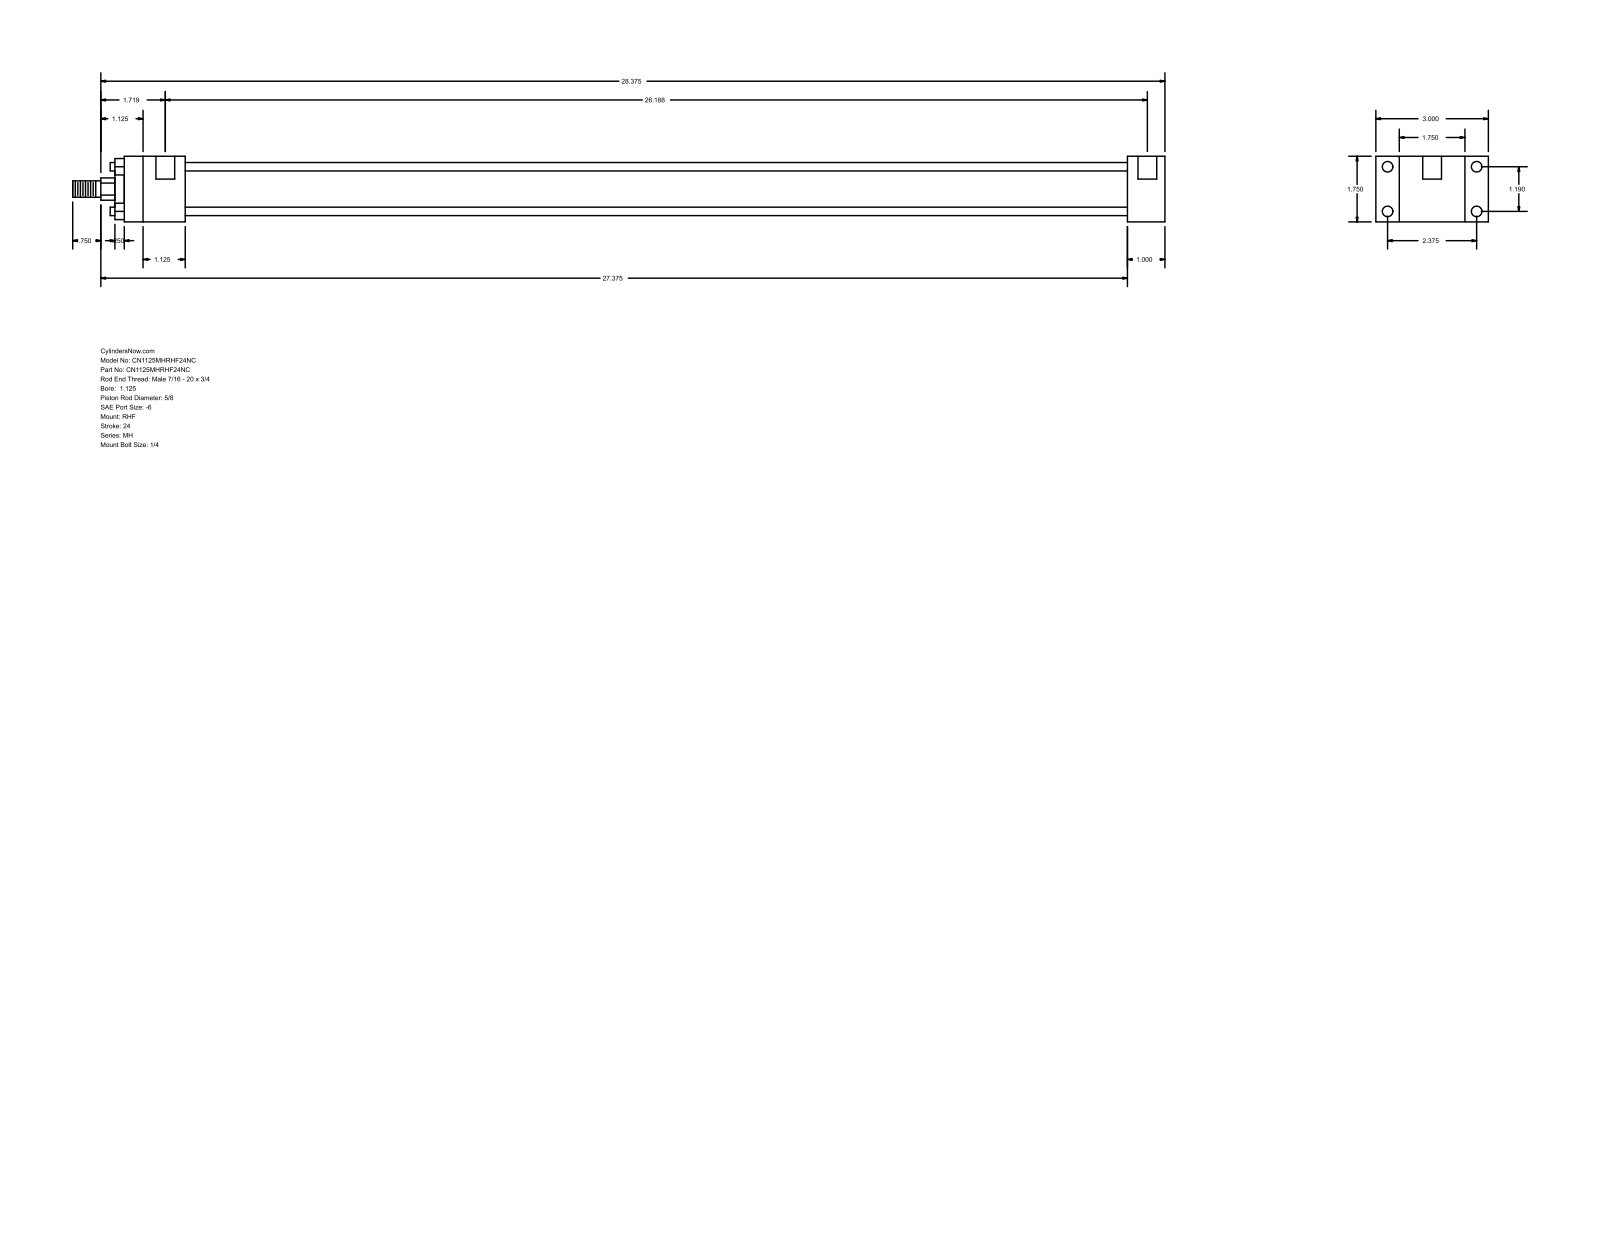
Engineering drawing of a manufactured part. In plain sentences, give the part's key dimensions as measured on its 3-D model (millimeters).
The part is named "MH_RHF__0112_0.625". Its 3-D file was written by "GSSL Pune (CONFIG_CONTROL_DESIGN)". It is 0 solids with 88 faces: 60 planar, 28 cylindrical and 0 other. Overall it measures 739.77 by 76.2 by 44.45 millimeters. Round holes: 4 of diameter 5.56, 4 of diameter 7.14, 2 of diameter 12.7. Round bosses or shafts: 4 of diameter 5.71, 1 of diameter 34.92, 1 of diameter 28.57, 1 of diameter 15.88, 1 of diameter 11.11. Partial cylindrical surfaces (rounded edges, fillets, slot ends): 1 of radius 7.54. The main face-to-face distances are 44.46, 15.87, 25.4, 60.33, 76.2, 638.18, 663.58, 41.27, 679.45, 704.85. The hole center spacings are 30.22, 60.32, 67.47, 661.99, 3.17, 665.16.
